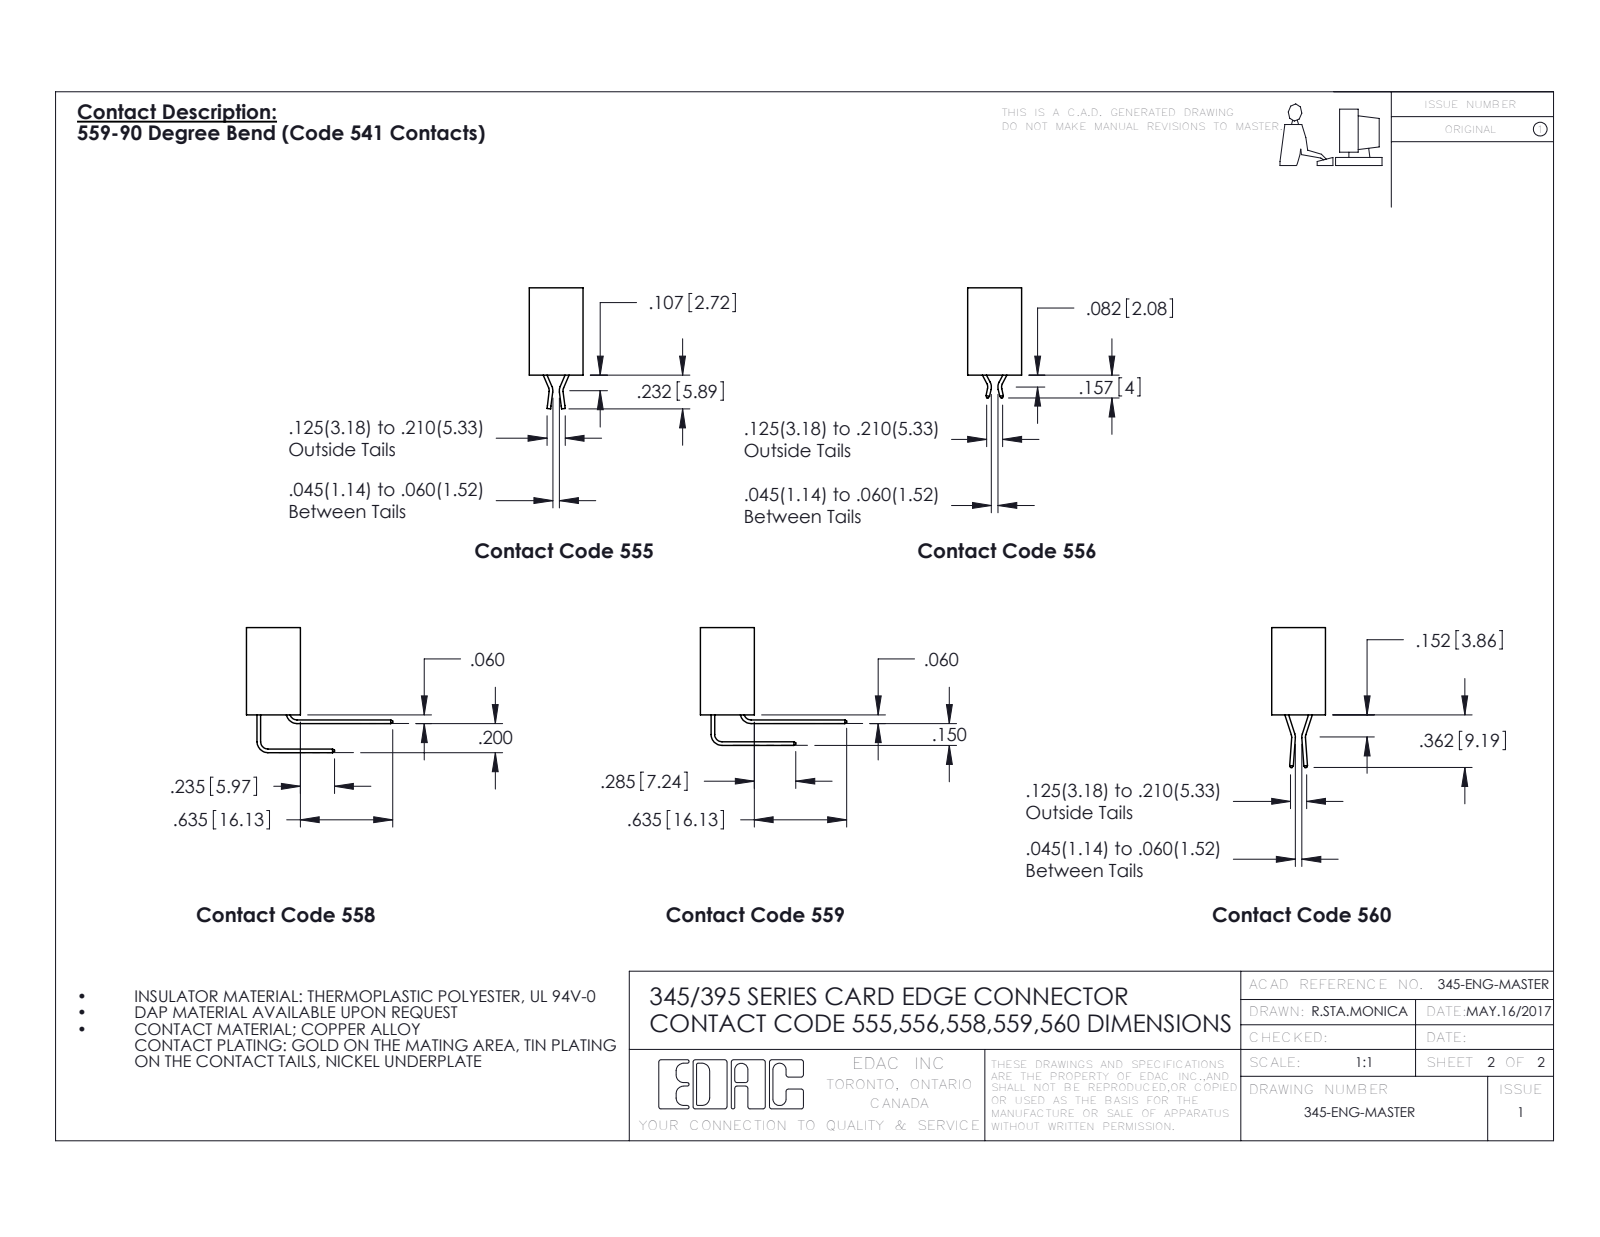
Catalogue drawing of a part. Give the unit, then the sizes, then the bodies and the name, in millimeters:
Units: millimetres
Overall size (bounding box): 31.3 × 24.4 × 9.4
Round holes (diameter × count): ⌀1.6 ×1
Partial cylindrical surfaces — rounded edges, fillets, slot ends (radius × count): R0.3 ×22, R0.2 ×14, R0.3 ×14, R0.2 ×6, R0.8 ×6, R0.7 ×3, R0.8 ×2, R1 ×2
Main face-to-face distances: 5.1, 7.6, 1.8, 2.5, 9.4, 2.5, 6.9, 0.6, 7.6, 1.5
Volume: 2 620 mm³ · Surface area: 3 307 mm²
Bodies: 8 solids, 524 faces (356 planar, 168 cylindrical, 0 other)
Part name (STEP PRODUCT): 395-007-542-101; 345-292-001_345-293-142; 345 Part_No Mounting Lugs
STEP written by: SolidWorks 2016 (CONFIG_CONTROL_DESIGN)
